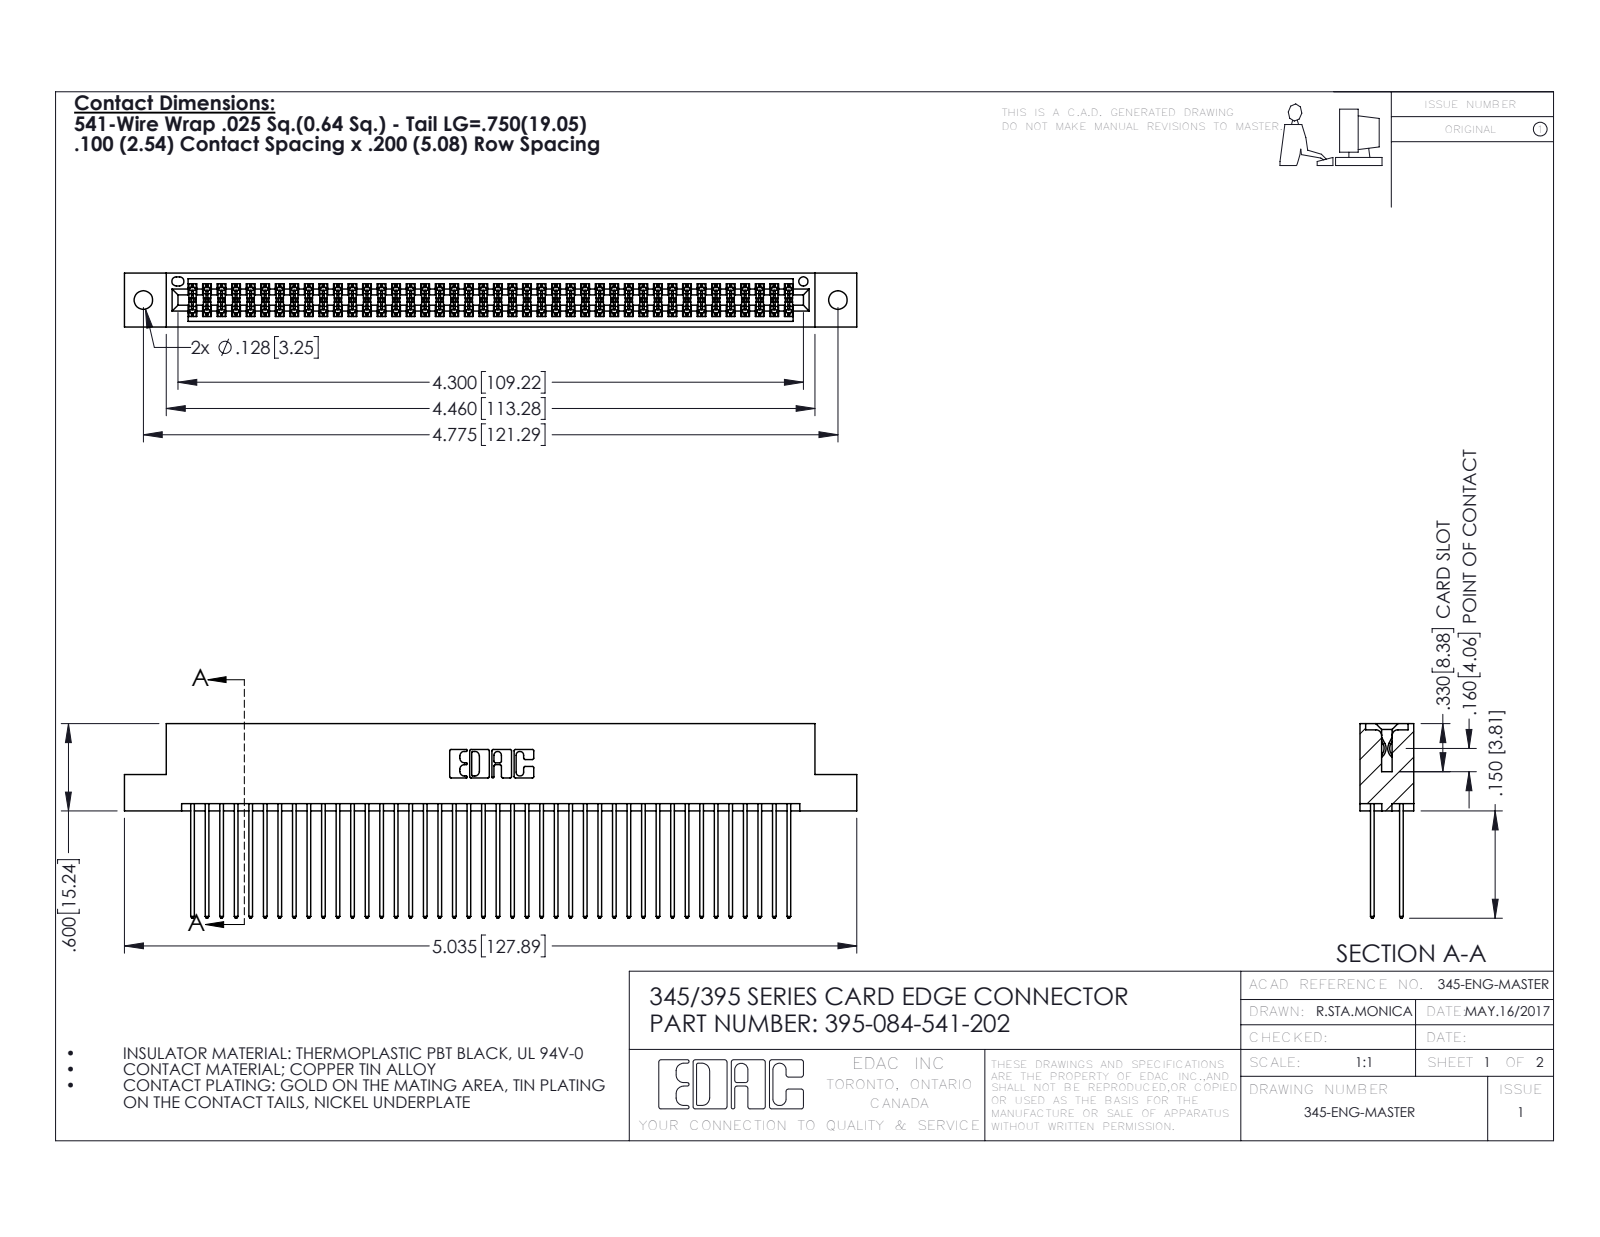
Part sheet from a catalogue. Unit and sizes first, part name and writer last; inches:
Units: inches
Overall size (bounding box): 5.035 × 1.337 × 0.37
Round holes (diameter × count): ⌀0.128 ×2, ⌀0.064 ×1
Partial cylindrical surfaces — rounded edges, fillets, slot ends (radius × count): R0.006 ×126, R0.01 ×84, R0.01 ×22, R0.007 ×6, R0.031 ×6, R0.026 ×3, R0.014 ×2, R0.019 ×2
Main face-to-face distances: 0.298, 0.072, 0.2, 0.098, 0.272, 0.025, 0.225, 0.37, 0.175, 0.149
Hole centre spacings: 0.27, 4.539, 4.775
Volume: 0.785 in³ · Surface area: 32.57 in²
Bodies: 85 solids, 4326 faces (2852 planar, 1474 cylindrical, 0 other)
Part name (STEP PRODUCT): 395-084-541-202; 345-292-001_345-293-141; 345 Part_Flush Mounting Lugs - 0.128 Dia
STEP written by: SolidWorks 2016 (CONFIG_CONTROL_DESIGN)
